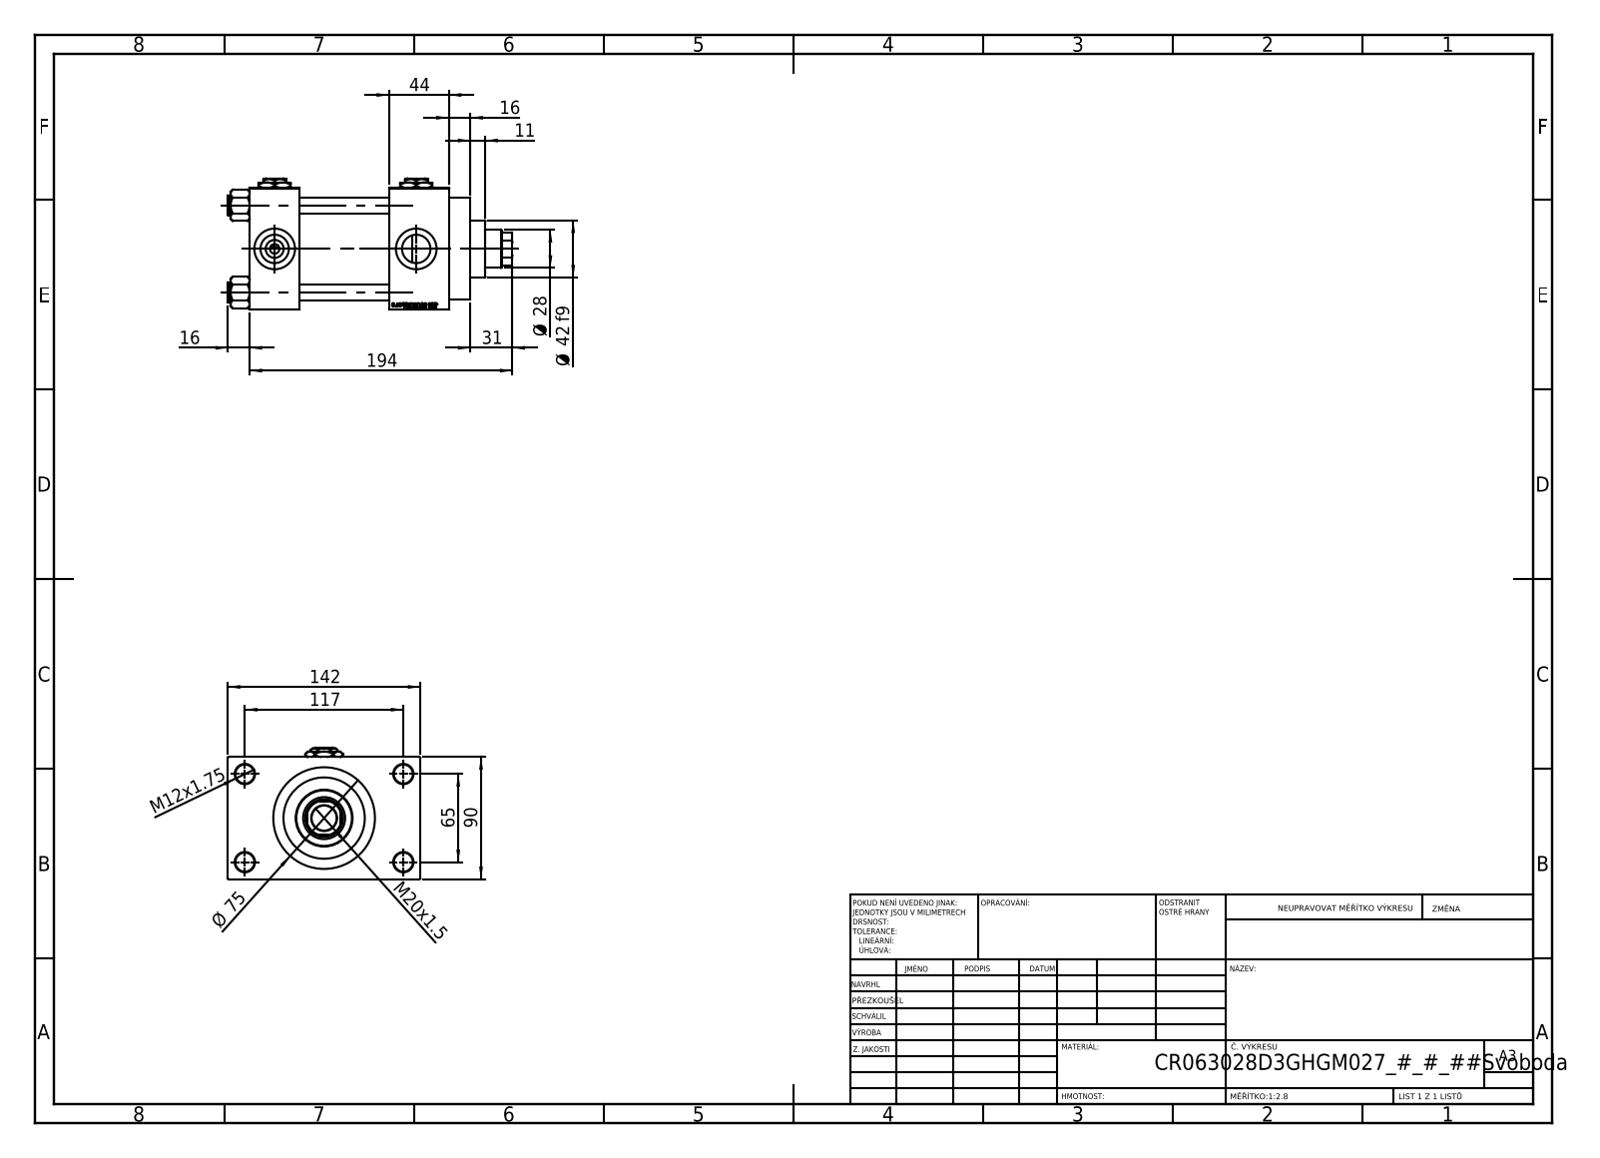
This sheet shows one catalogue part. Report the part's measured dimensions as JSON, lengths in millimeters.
{"part_name": "Zatka_pro_OIL_PORT; V215CR_D_Body; V215_VC_A; V215CR_D_TYCINKA (+2 more)", "step_written_by": "SolidWorks 2019 (CONFIG_CONTROL_DESIGN)", "units": "millimeters", "bodies": {"solids": 13, "faces": 1204, "planar": 545, "cylindrical": 99, "other": 560}, "overall_size": [210, 142, 97], "volume_mm3": 1103000, "surface_area_mm2": 209516, "round_holes": [[12, 4], [14, 4], [20.96, 4], [30, 4], [7, 3], [18.5, 1], [28, 1], [31, 1], [50, 1], [60, 1], [63, 1]], "round_bosses_or_shafts": [[15, 4], [75, 1], [69, 1], [42, 1]], "partial_cylinders_radius": [[13.5, 1]], "face_to_face_distances": [90, 66, 37, 103, 110, 147, 44, 116, 26, 16], "hole_center_spacings": [26.35, 45.47, 64.3, 66.92, 69.81, 90.65, 111.34, 65]}
